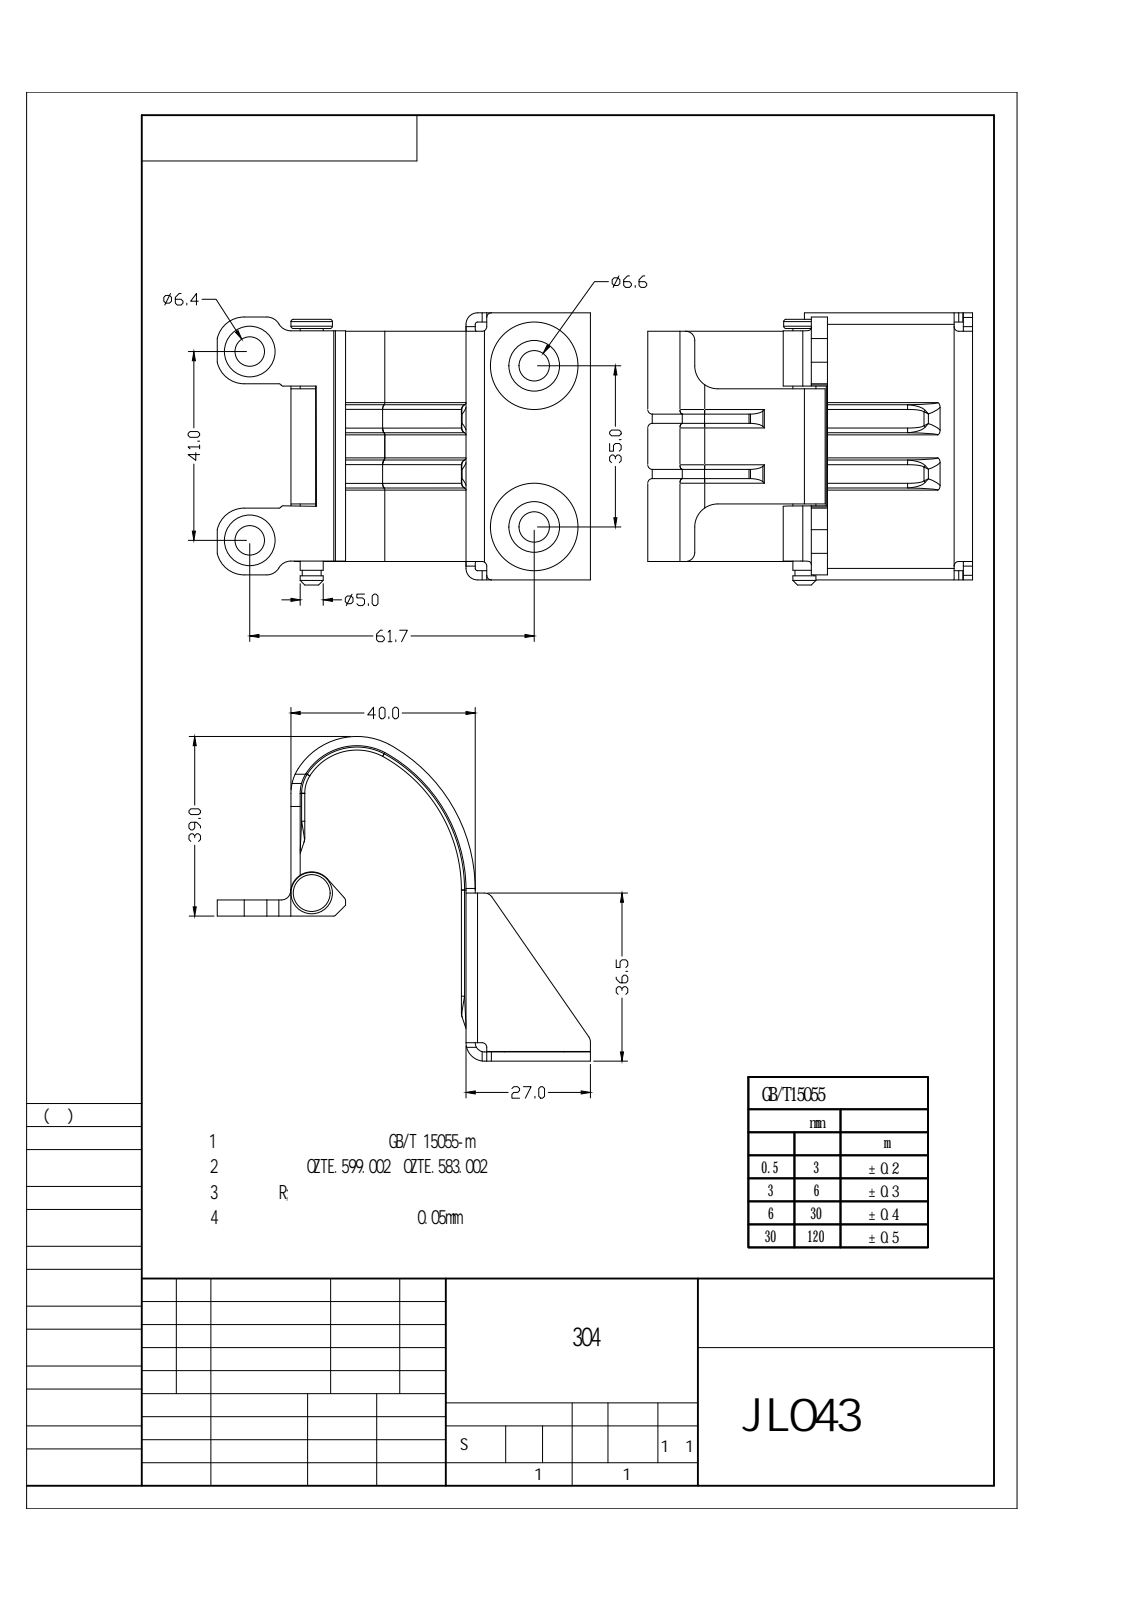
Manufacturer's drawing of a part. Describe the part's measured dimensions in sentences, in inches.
The part is named "010_dwg". Its 3-D file was written by "SIEMENS PLM Software NX 8.5 (CONFIG_CONTROL_DESIGN)". It is 3 solids with 315 faces: 79 planar, 125 cylindrical and 111 other. Overall it measures 3.189 by 2.776 by 2.327 inches. Its volume is 1.319 cubic inches and its surface area 35.37 square inches. Round holes: 2 of diameter 0.236, 2 of diameter 0.252, 2 of diameter 0.433, 1 of diameter 0.205. Round bosses or shafts: 1 of diameter 0.354, 1 of diameter 0.197, 1 of diameter 0.161. Partial cylindrical surfaces (rounded edges, fillets, slot ends): 21 of radius 0.039, 16 of radius 0.02, 8 of radius 0.043, 7 of radius 0.079, 6 of radius 0.118, 4 of radius 0.236, 2 of radius 0.098, 2 of radius 0.197. The main face-to-face distances are 0.079, 2.205, 1.496, 2.126, 1.24, 1.161, 1.378, 0.039, 2.283, 1.417. The hole center spacings are 1.378, 1.614, 2.434, 2.434, 2.853, 2.856.
